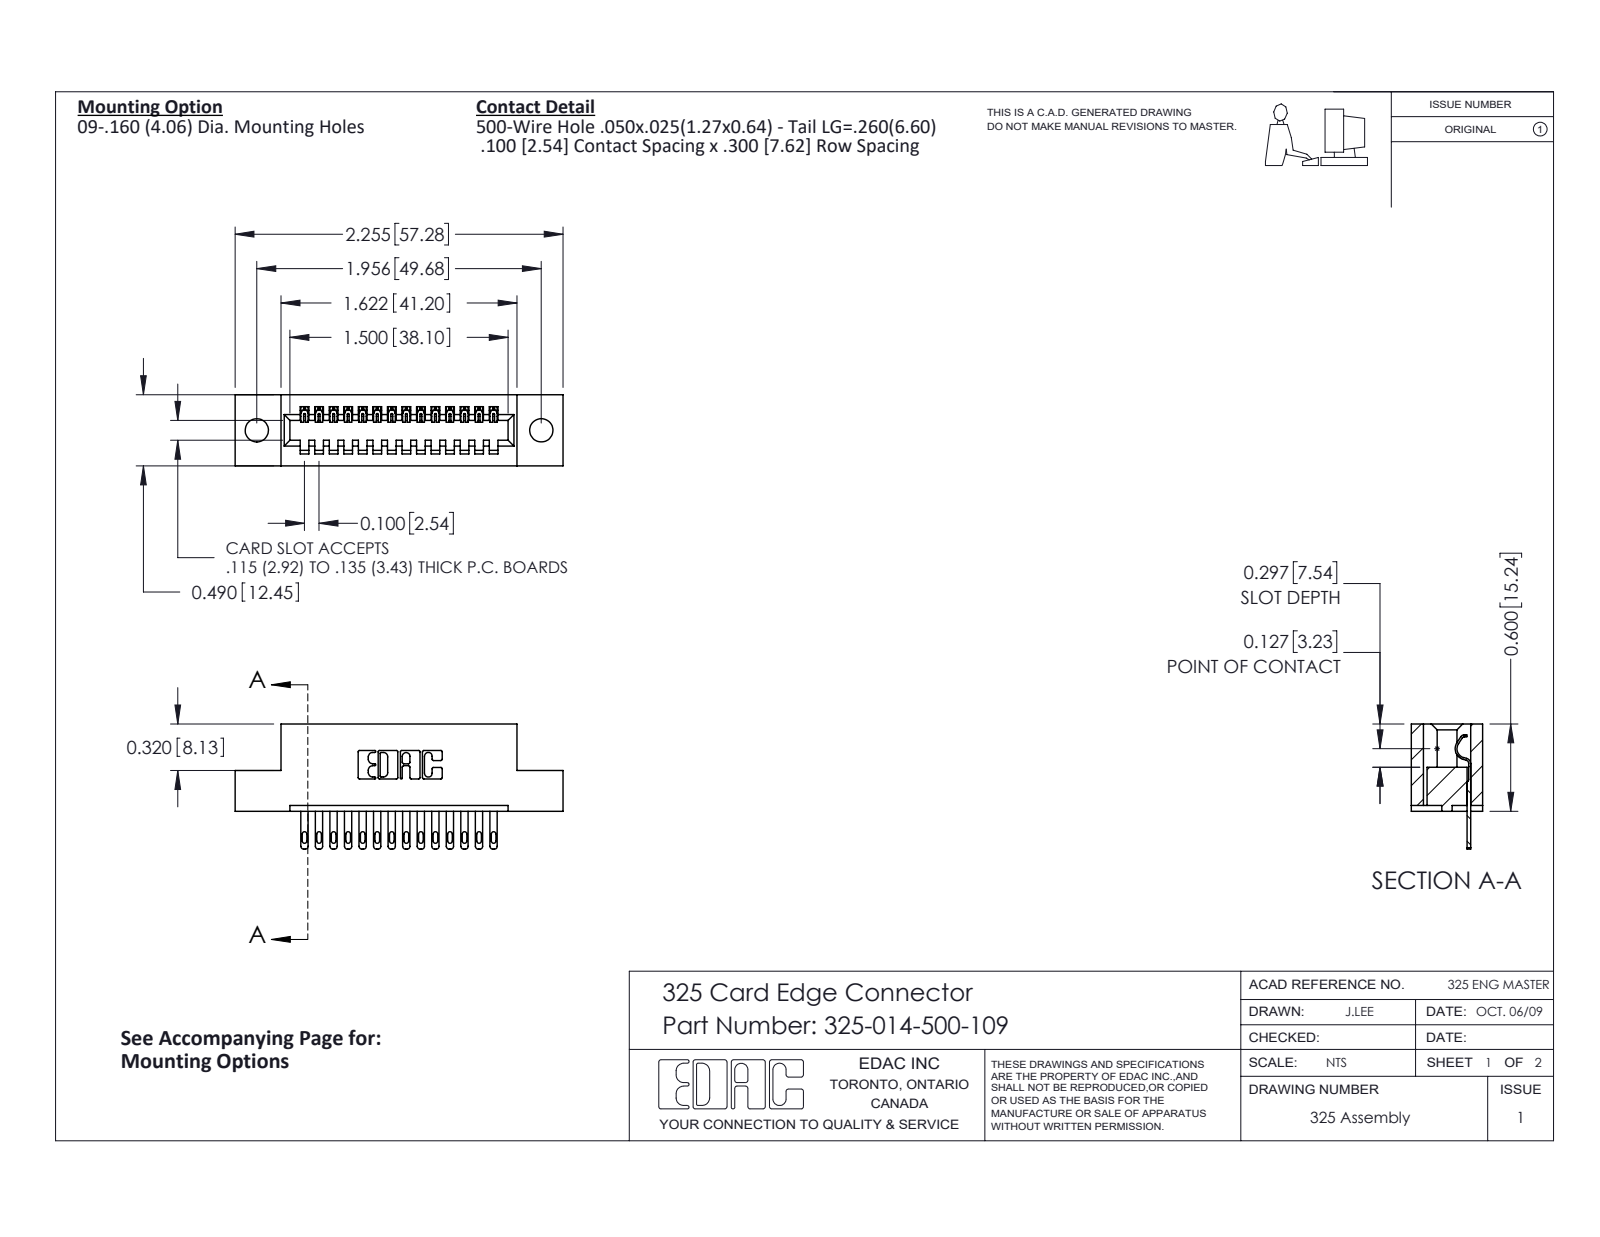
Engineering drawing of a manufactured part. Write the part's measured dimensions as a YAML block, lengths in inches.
part_name: "325-014-500-109; 325 Part_.160 TH; 325-292-001_325-293-100"
step_written_by: "SolidWorks 2016 (CONFIG_CONTROL_DESIGN)"
units: inches
bodies: {solids: 15, faces: 870, planar: 574, cylindrical: 296, other: 0}
overall_size: [2.255, 0.86, 0.49]
volume: 0.417
surface_area: 10.72
round_holes:
  - {diameter: 0.16, count: 2}
partial_cylinders:
  - {radius: 0.006, count: 28}
  - {radius: 0.016, count: 28}
  - {radius: 0.02, count: 28}
  - {radius: 0.01, count: 22}
  - {radius: 0.007, count: 6}
  - {radius: 0.031, count: 6}
  - {radius: 0.026, count: 3}
  - {radius: 0.014, count: 1}
face_to_face_distances: [0.083, 0.407, 0.3, 0.49, 0.04, 0.107, 0.383, 0.025, 0.1, 0.6]
hole_center_spacings: [1.956]
